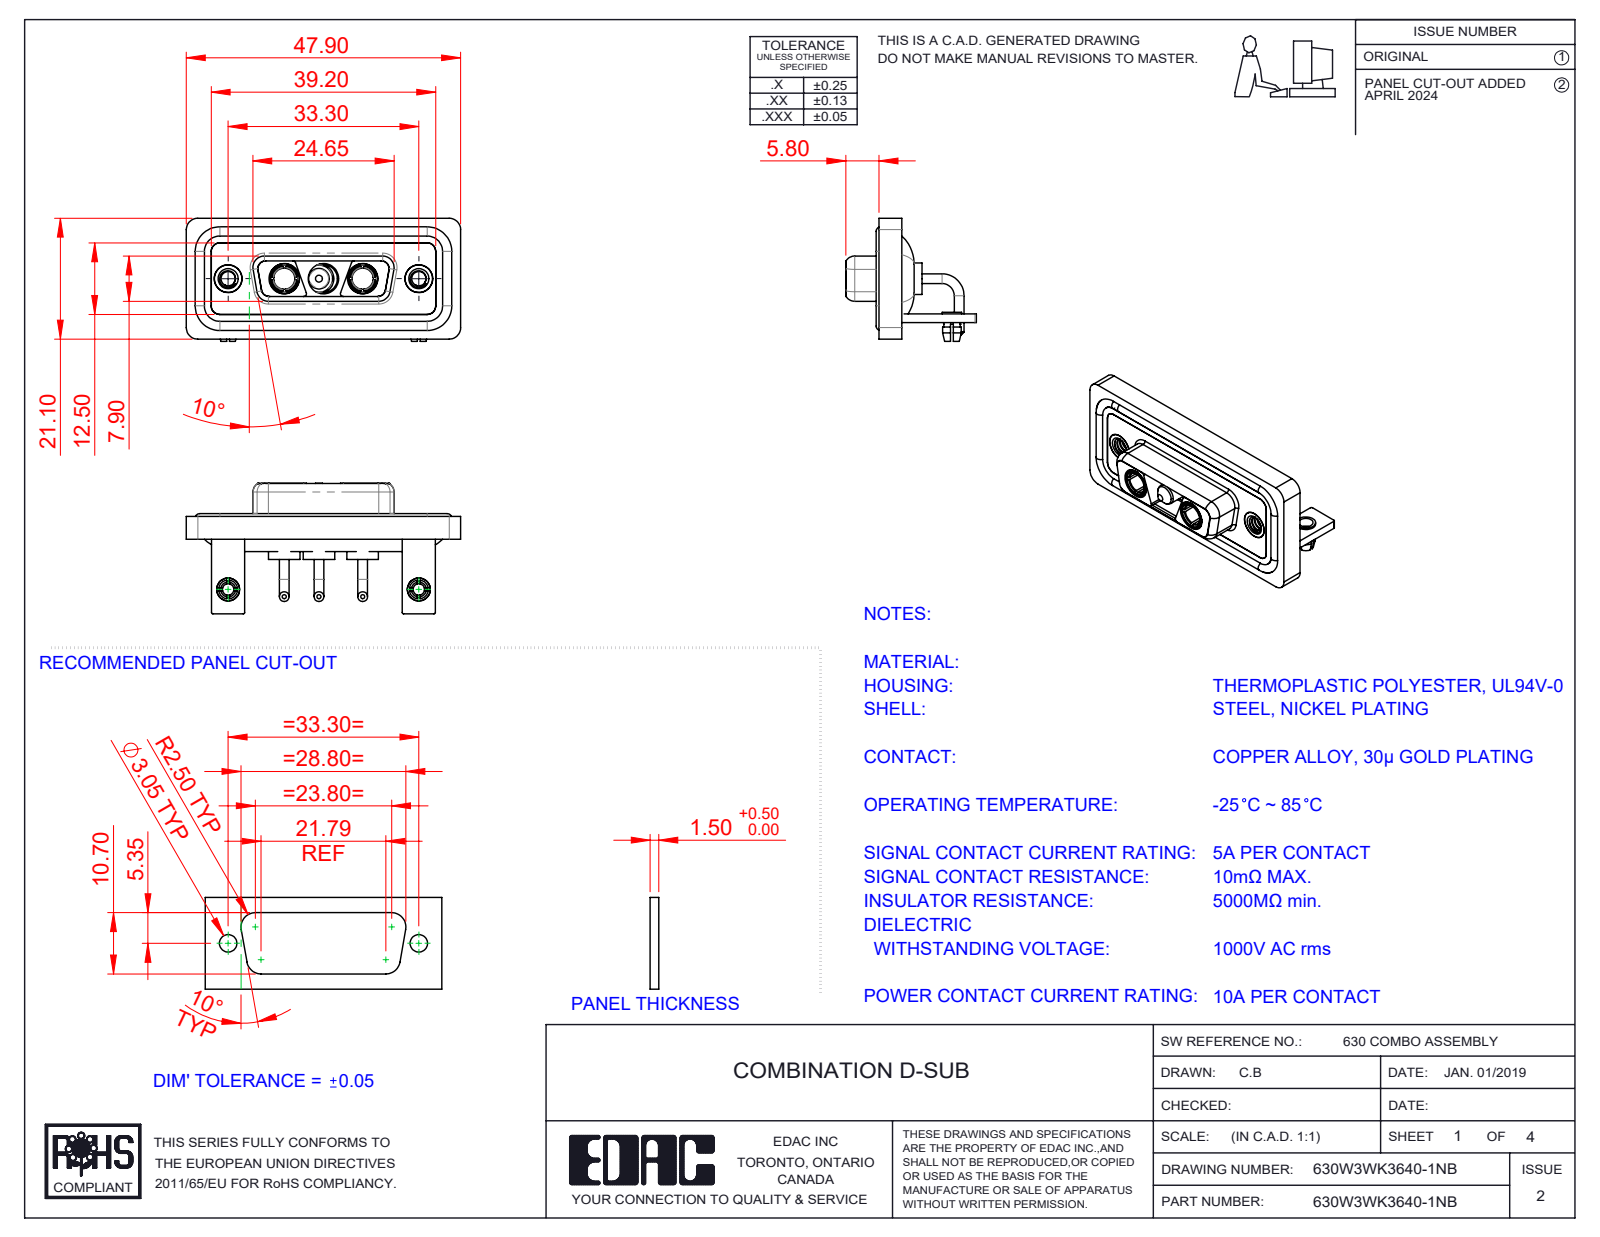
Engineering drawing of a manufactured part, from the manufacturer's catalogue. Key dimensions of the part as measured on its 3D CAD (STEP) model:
Part name (STEP PRODUCT): 630Combo Shell Rear_15 Contacts; 630Combo Board Lock_50 Contacts; Power Pin_10A RA; 630Combo Threaded Rivet_A (+6 more)
STEP written by: SolidWorks 2023 (CONFIG_CONTROL_DESIGN)
Units: millimetres
Bodies: 17 solids, 729 faces (246 planar, 318 cylindrical, 165 other)
Overall size (bounding box): 47.9 × 22.8 × 21.5
Volume: 6 254 mm³ · Surface area: 10 535 mm²
Round holes (diameter × count): ⌀4.85 ×5, ⌀2.5 ×4, ⌀5.3 ×3, ⌀2 ×2, ⌀3.2 ×2, ⌀3.7 ×2, ⌀4 ×2, ⌀4.05 ×2, ⌀5 ×2
Round bosses / shafts (diameter × count): ⌀1.7 ×6, ⌀1.6 ×4, ⌀5.5 ×3, ⌀5.2 ×3, ⌀4.75 ×3, ⌀3.75 ×3, ⌀4.96 ×2, ⌀4.95 ×2
Partial cylindrical surfaces — rounded edges, fillets, slot ends (radius × count): R2 ×21, R1.5 ×18, R0.25 ×16, R1.35 ×12, R0.5 ×9, R1.6 ×8, R0.6 ×4, R0.65 ×4
Main face-to-face distances: 0.4, 2.9, 1.5, 3.7, 1.8, 1.1, 4.1, 1.6, 2.5, 1.4
Hole centre spacings: 6.85, 9.8, 16.65, 23.5, 33.3, 13.7
